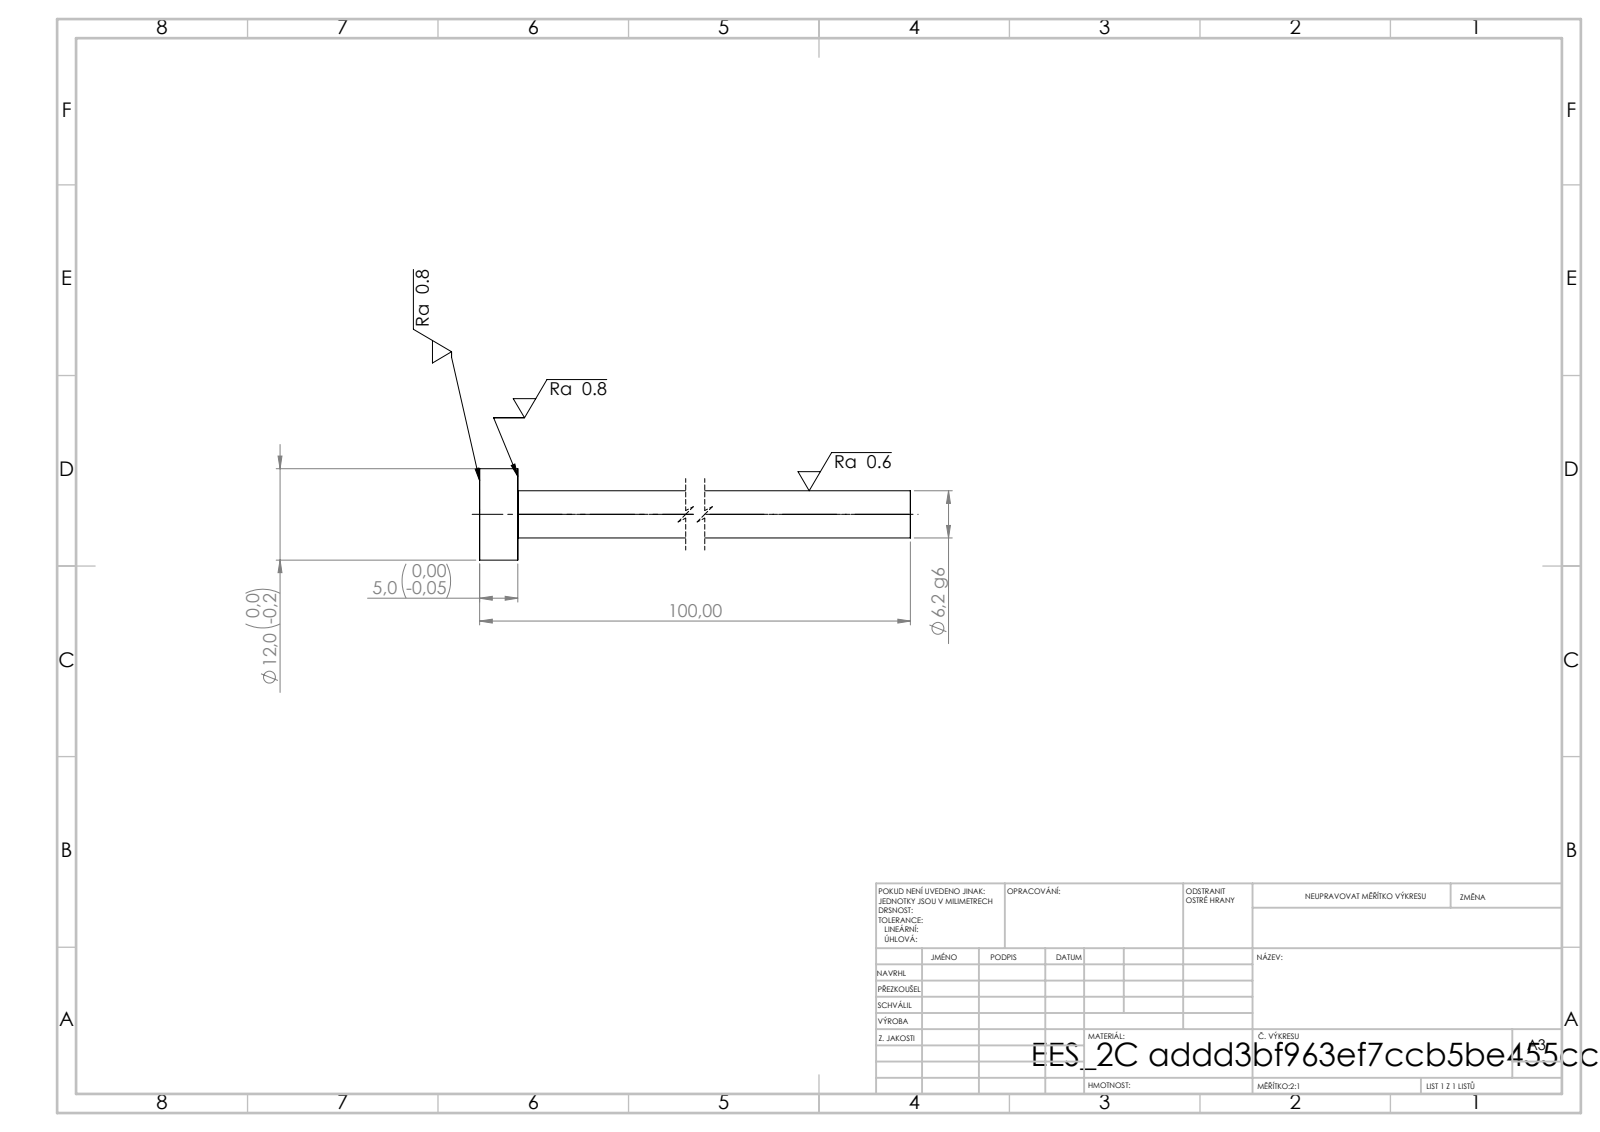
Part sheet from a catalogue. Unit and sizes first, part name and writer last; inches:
Units: inches
Overall size (bounding box): 3.937 × 0.472 × 0.472
Round bosses / shafts (diameter × count): ⌀0.472 ×1, ⌀0.244 ×1
Main face-to-face distances: 0.197, 3.937, 3.74
Volume: 0.21 in³ · Surface area: 3.511 in²
Bodies: 1 solid, 7 faces (3 planar, 4 cylindrical, 0 other)
STEP written by: SolidWorks 2019 (CONFIG_CONTROL_DESIGN)
